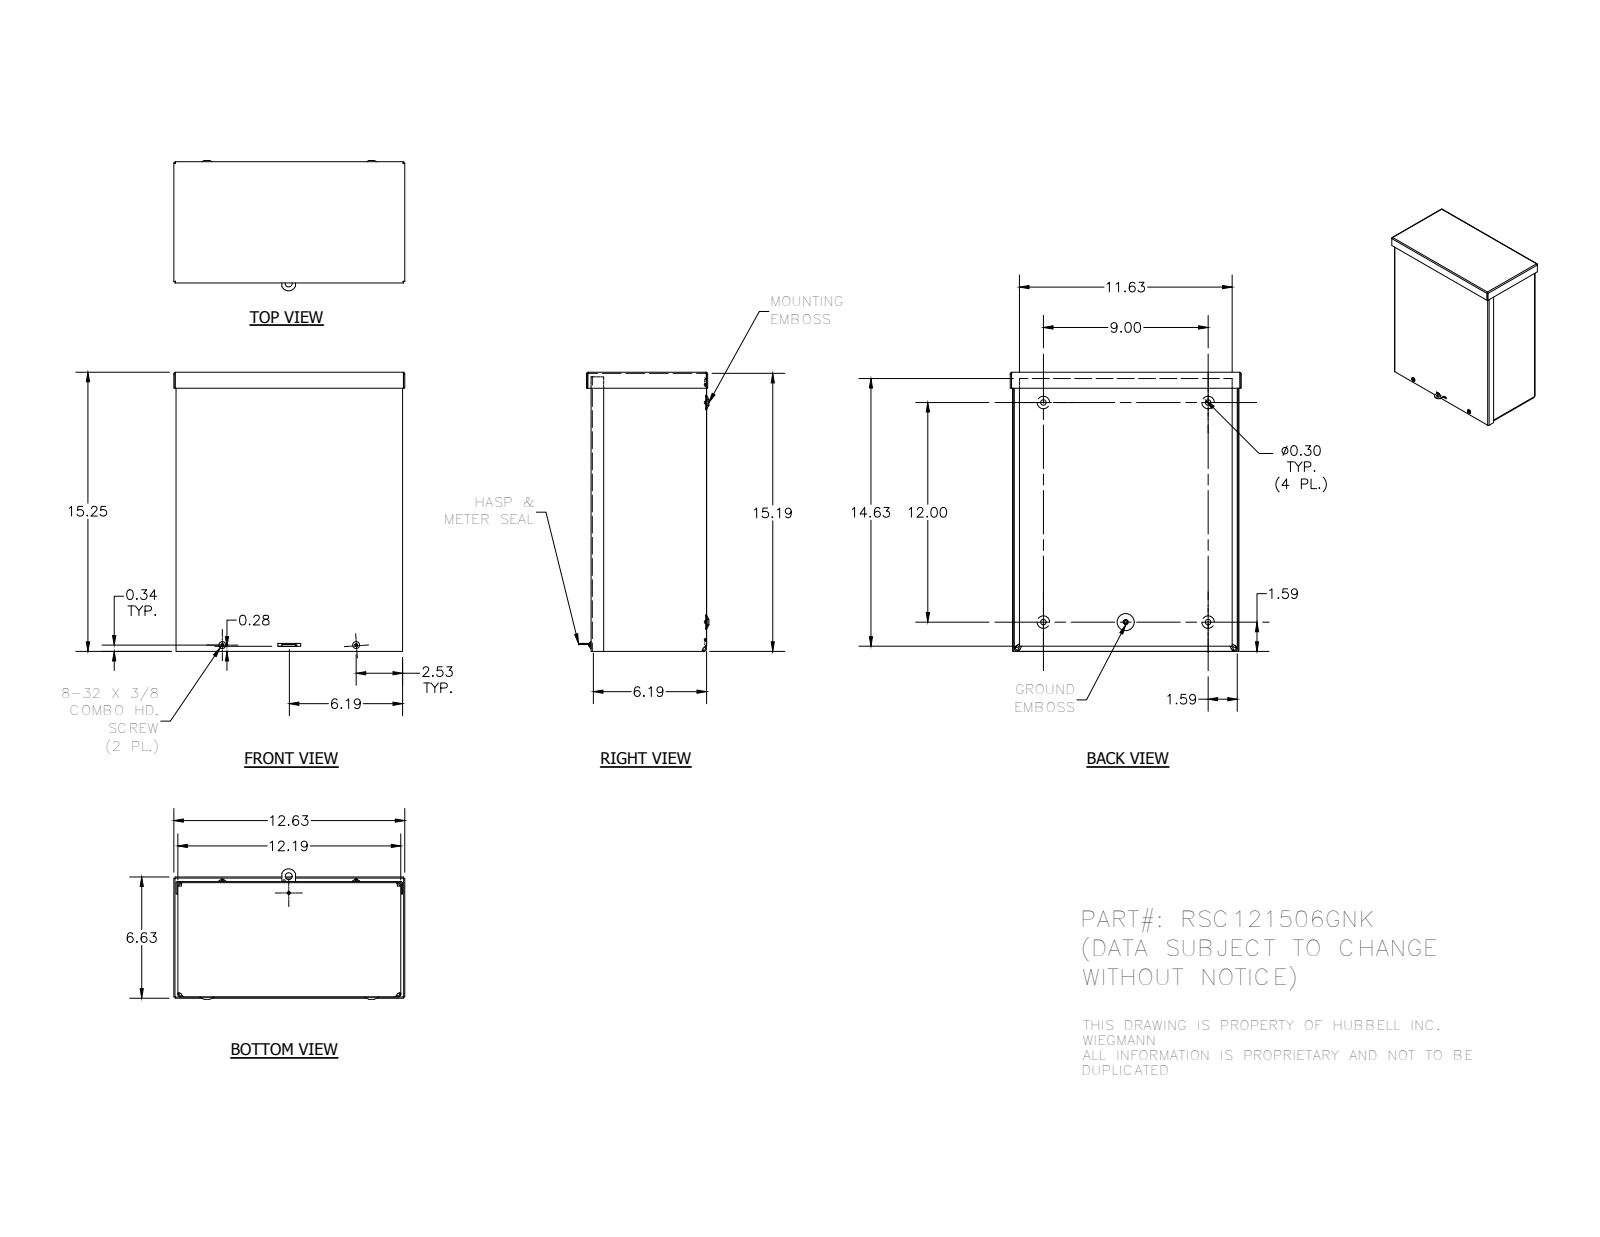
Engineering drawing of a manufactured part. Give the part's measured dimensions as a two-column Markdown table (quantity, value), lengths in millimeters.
| quantity | value |
| --- | --- |
| part name | RSC121506GNK_WRAP; RSC1215GNK_LID; RSC1206GNK_CAP; 3183 (+3 more) |
| STEP written by | Autodesk Inventor 2014 (AUTOMOTIVE_DESIGN) |
| units | millimeters |
| bodies | 7 solids, 377 faces (163 planar, 78 cylindrical, 136 other) |
| overall size | 387.36 × 320.68 × 180.97 |
| volume | 916 200 mm³ |
| surface area | 1 175 000 mm² |
| round holes (diameter × count) | 7.62 × 4, 7.95 × 4, 3.17 × 2, 3.76 × 2, 3.96 × 1, 4.19 × 1, 9.52 × 1 |
| round bosses / shafts (diameter × count) | 9.75 × 2, 4.17 × 2, 5.8 × 1 |
| partial cylindrical surfaces (radius × count) | 0.79 × 8, 2.37 × 8, 3.17 × 8, 4.75 × 8, 1.4 × 4, 1.57 × 4, 2.38 × 4, 2.97 × 4 |
| main face-to-face distances | 1.58, 1.57, 158.73, 157.15, 307.99, 1.59, 160.32, 158.74, 384.19, 3.15 |
| hole center spacings | 34.43, 114.3, 185.75, 228.6, 304.8, 325.52, 332.44, 337.26 |
